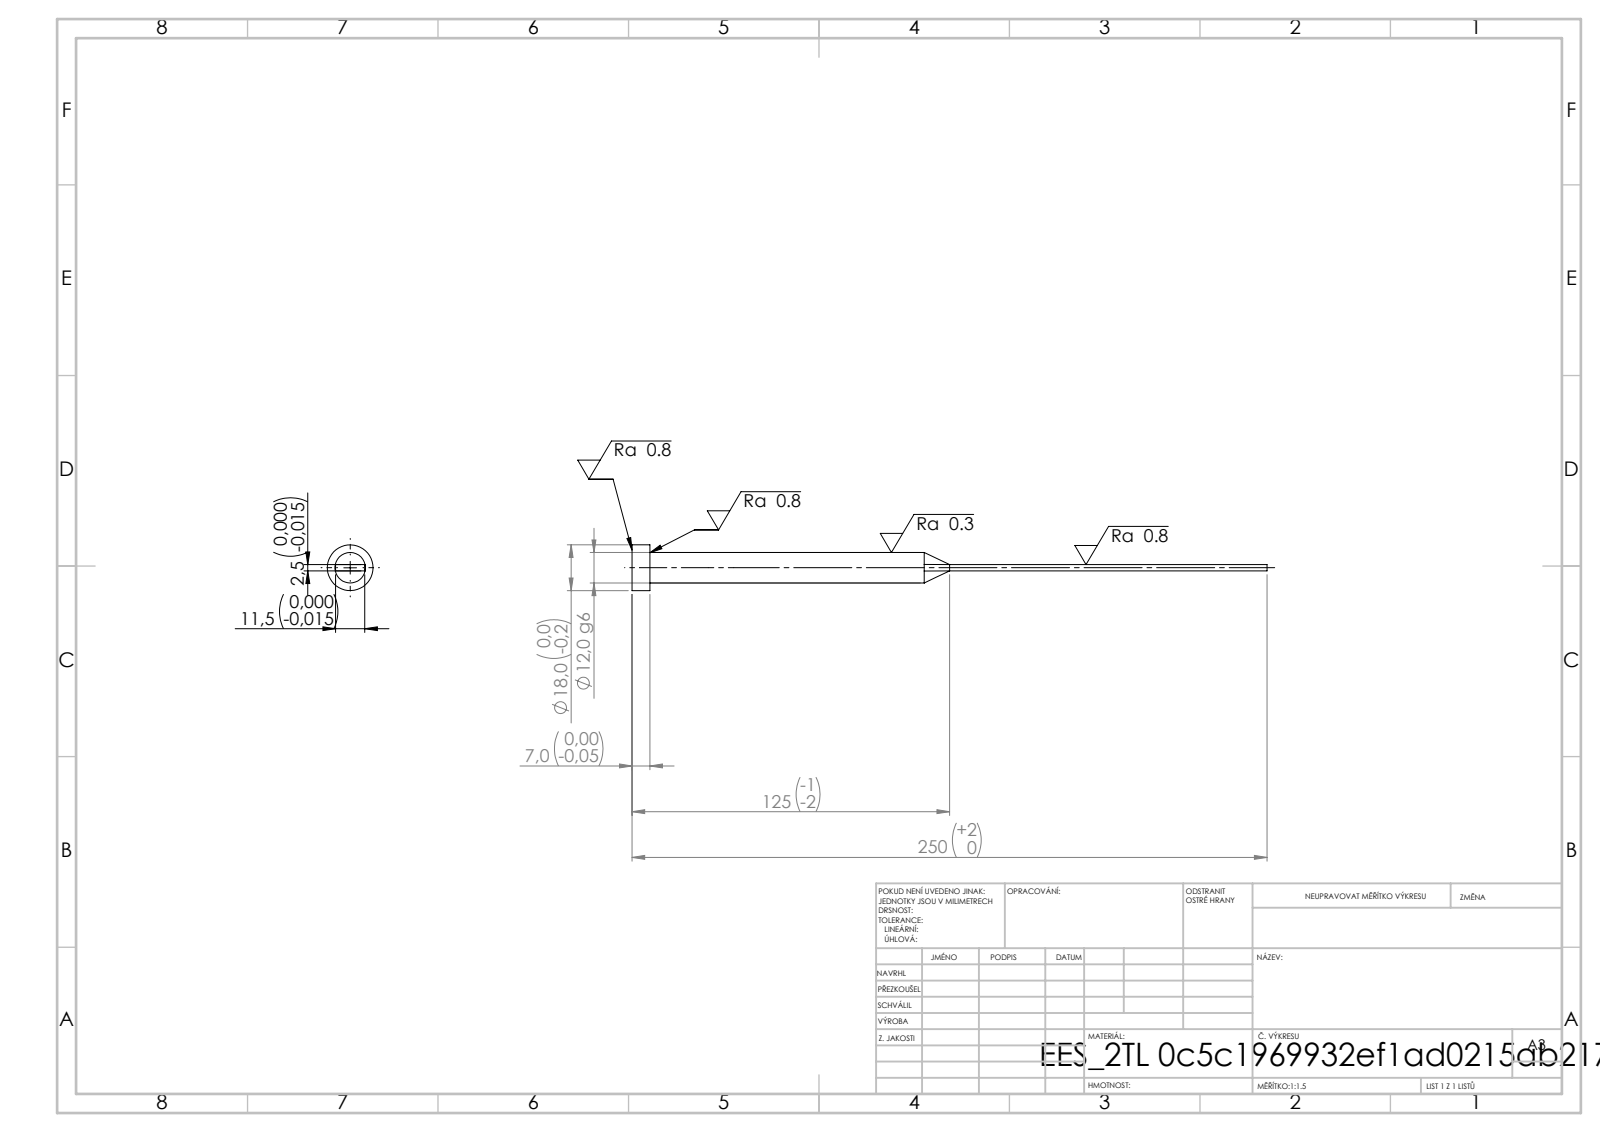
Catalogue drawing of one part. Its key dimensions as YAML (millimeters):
step_written_by: "SolidWorks 2019 (CONFIG_CONTROL_DESIGN)"
units: millimeters
bodies: {solids: 1, faces: 15, planar: 7, cylindrical: 4, other: 4}
overall_size: [250, 18, 18]
volume: 18269
surface_area: 8721
round_bosses_or_shafts:
  - {diameter: 18, count: 1}
  - {diameter: 12, count: 1}
face_to_face_distances: [2.5, 11.5, 7, 250, 243]
